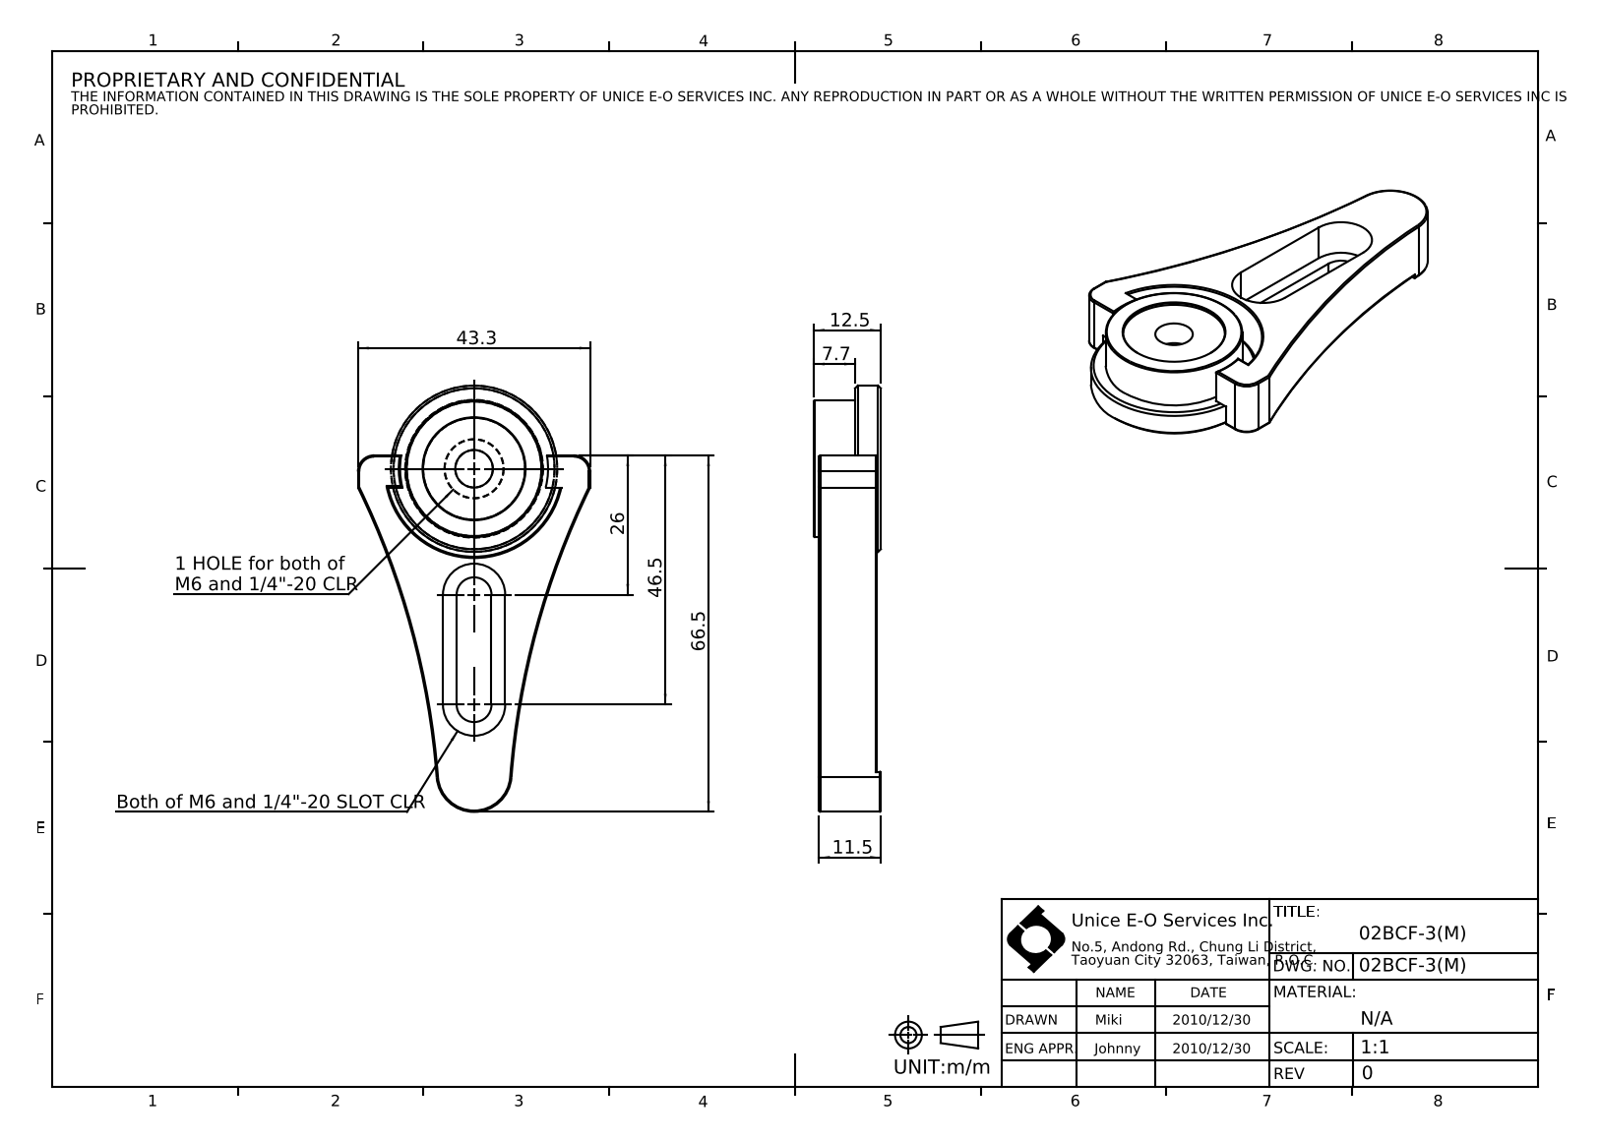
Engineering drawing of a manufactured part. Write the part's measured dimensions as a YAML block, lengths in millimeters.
part_name: "02BCF-3(M)"
step_written_by: "SolidWorks 2016 (CONFIG_CONTROL_DESIGN)"
units: millimeters
bodies: {solids: 2, faces: 93, planar: 26, cylindrical: 38, other: 29}
overall_size: [79.5, 43.3, 12.5]
volume: 16029
surface_area: 8033
round_holes:
  - {diameter: 7, count: 1}
  - {diameter: 11, count: 1}
  - {diameter: 19, count: 1}
  - {diameter: 25.5, count: 1}
round_bosses_or_shafts:
  - {diameter: 31, count: 1}
partial_cylinders:
  - {radius: 0.25, count: 7}
  - {radius: 3, count: 2}
  - {radius: 3.25, count: 2}
  - {radius: 5.8, count: 2}
  - {radius: 150, count: 2}
  - {radius: 7, count: 1}
  - {radius: 13.8, count: 1}
  - {radius: 16.4, count: 1}
face_to_face_distances: [0.5, 10.8, 11, 11.5, 12, 1, 0.7, 11.3, 4.5, 7.5]
